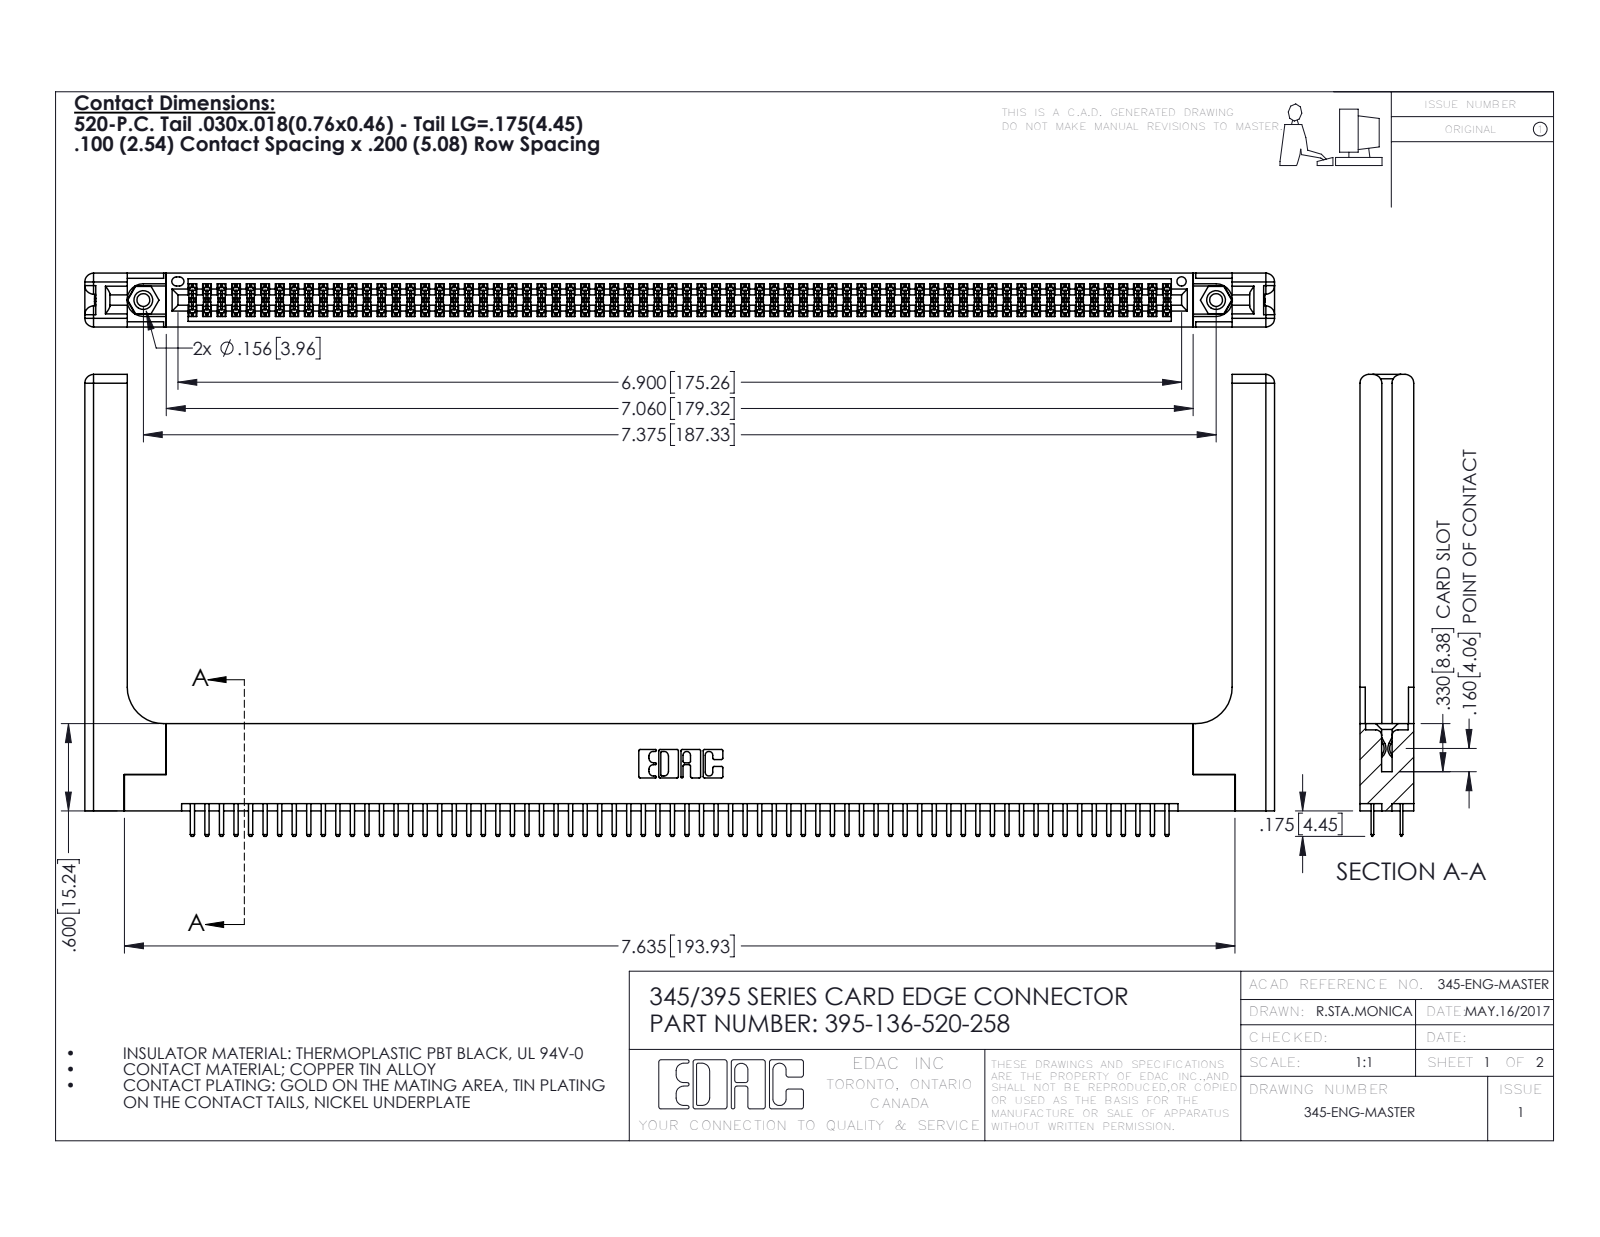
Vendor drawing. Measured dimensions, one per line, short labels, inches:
name: 345-250-001_345-250-001-102; 345 Part_Flush Mounting Lugs - 0.156 Dia-TH; 345-220-058_345-220-058; 345-292-001_345-293-120 (+1 more)
written by: SolidWorks 2016 (CONFIG_CONTROL_DESIGN)
unit: in
bodies: 141 solids, 7726 faces (4988 planar, 2678 cylindrical, 60 other)
size: 8.179 × 3.175 × 0.37
volume: 1.76 in³; area: 55.08 in²
holes: 2× ⌀0.089, 2× ⌀0.125, 2× ⌀0.156, 1× ⌀0.064
bosses: 2× ⌀0.155
rounds: 204× R0.006, 140× R0.01, 22× R0.01, 16× R0.06, 6× R0.007, 6× R0.031, 3× R0.026, 2× R0.014
face distances: 0.072, 0.298, 0.37, 0.2, 0.098, 0.272, 0.025, 0.225, 0.022, 0.072
hole spacings: 0.27, 7.139, 7.375
